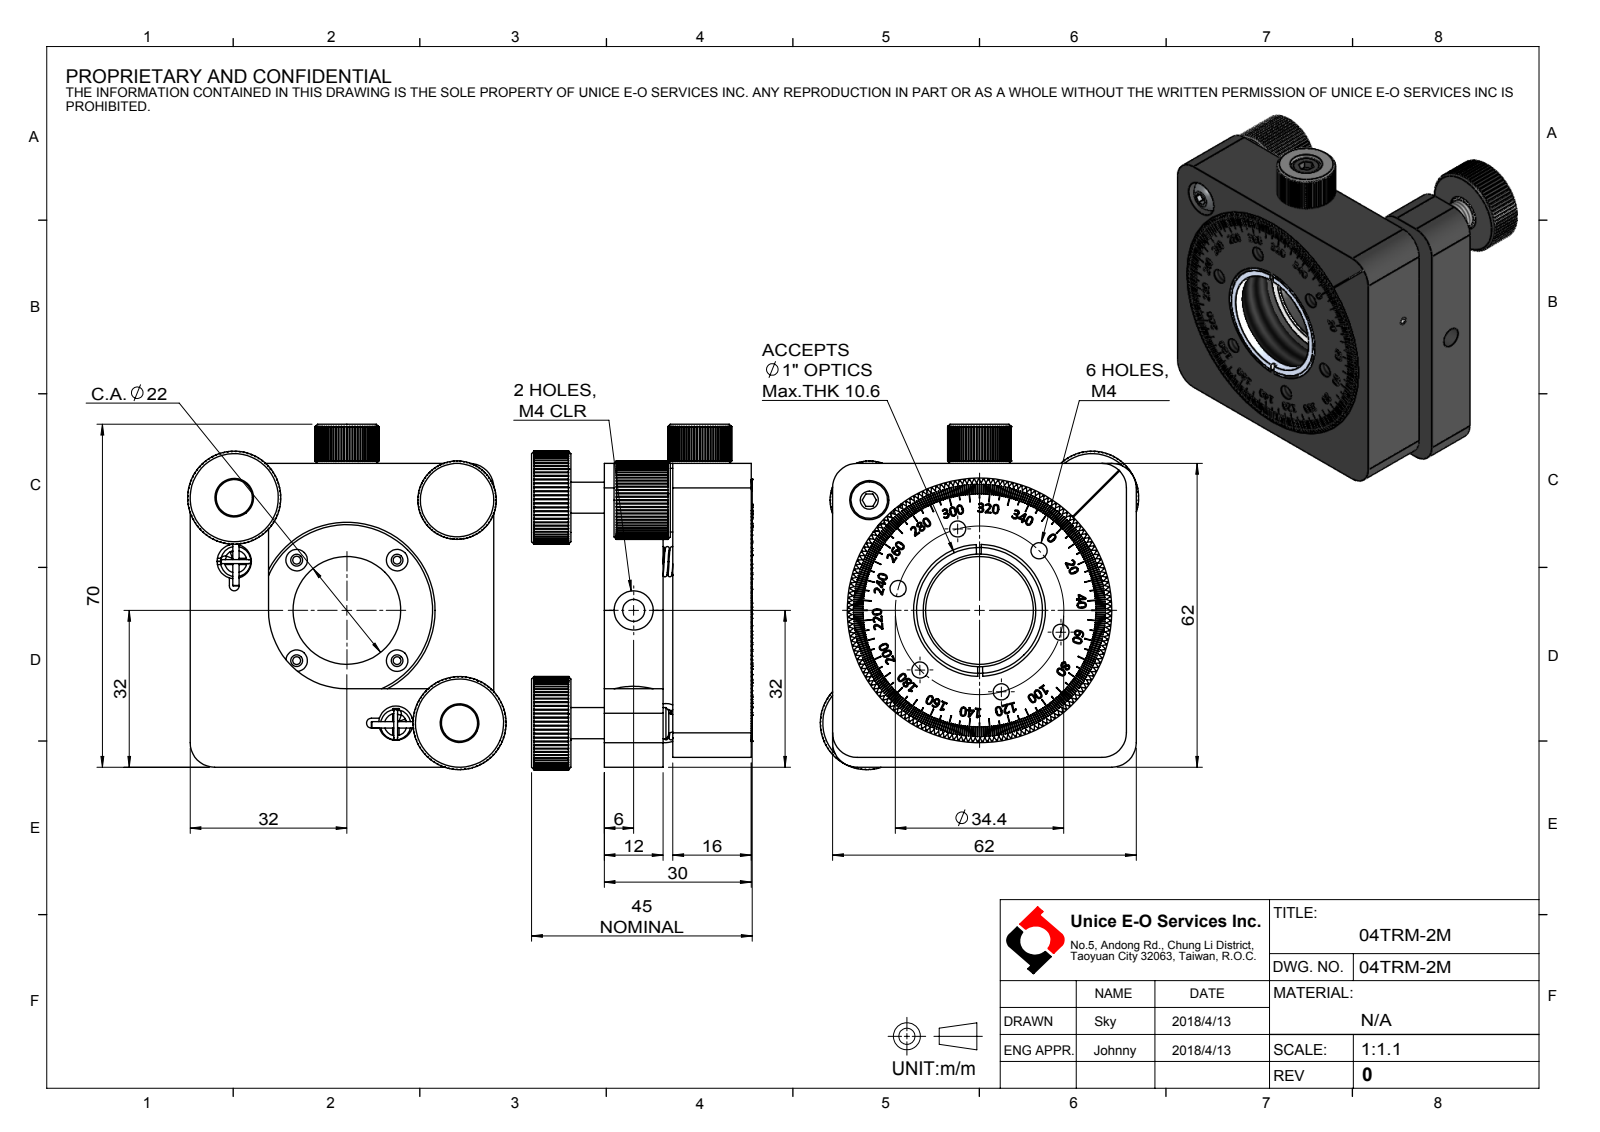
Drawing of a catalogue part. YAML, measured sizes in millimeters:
part_name: "04TRM-2M"
step_written_by: "SolidWorks 2016 (CONFIG_CONTROL_DESIGN)"
units: millimeters
bodies: {solids: 29, faces: 4206, planar: 2132, cylindrical: 1454, other: 620}
overall_size: [70.5, 65, 45.03]
volume: 75323
surface_area: 41644
round_holes:
  - {diameter: 3.3, count: 8}
  - {diameter: 1, count: 4}
  - {diameter: 1.6, count: 4}
  - {diameter: 2.4, count: 4}
  - {diameter: 4.4, count: 4}
  - {diameter: 4, count: 3}
  - {diameter: 8, count: 3}
  - {diameter: 1.7, count: 2}
  - {diameter: 4.5, count: 2}
  - {diameter: 6, count: 2}
  - {diameter: 6.35, count: 2}
  - {diameter: 7, count: 2}
round_bosses_or_shafts:
  - {diameter: 1.3, count: 4}
  - {diameter: 0.8, count: 4}
  - {diameter: 8, count: 2}
  - {diameter: 1.5, count: 2}
  - {diameter: 35, count: 1}
  - {diameter: 26.93, count: 1}
  - {diameter: 25.5, count: 1}
  - {diameter: 11, count: 1}
partial_cylinders:
  - {radius: 0.1, count: 288}
  - {radius: 5, count: 9}
  - {radius: 0.75, count: 4}
  - {radius: 1, count: 4}
  - {radius: 9.5, count: 2}
  - {radius: 1.5, count: 1}
  - {radius: 6.5, count: 1}
  - {radius: 8, count: 1}
face_to_face_distances: [8, 2, 5, 14, 12, 16, 10, 60, 22, 8.2]
hole_center_spacings: [17.2, 17.21, 8.61, 14.5, 16.02, 20.5, 22.49, 27.49]
